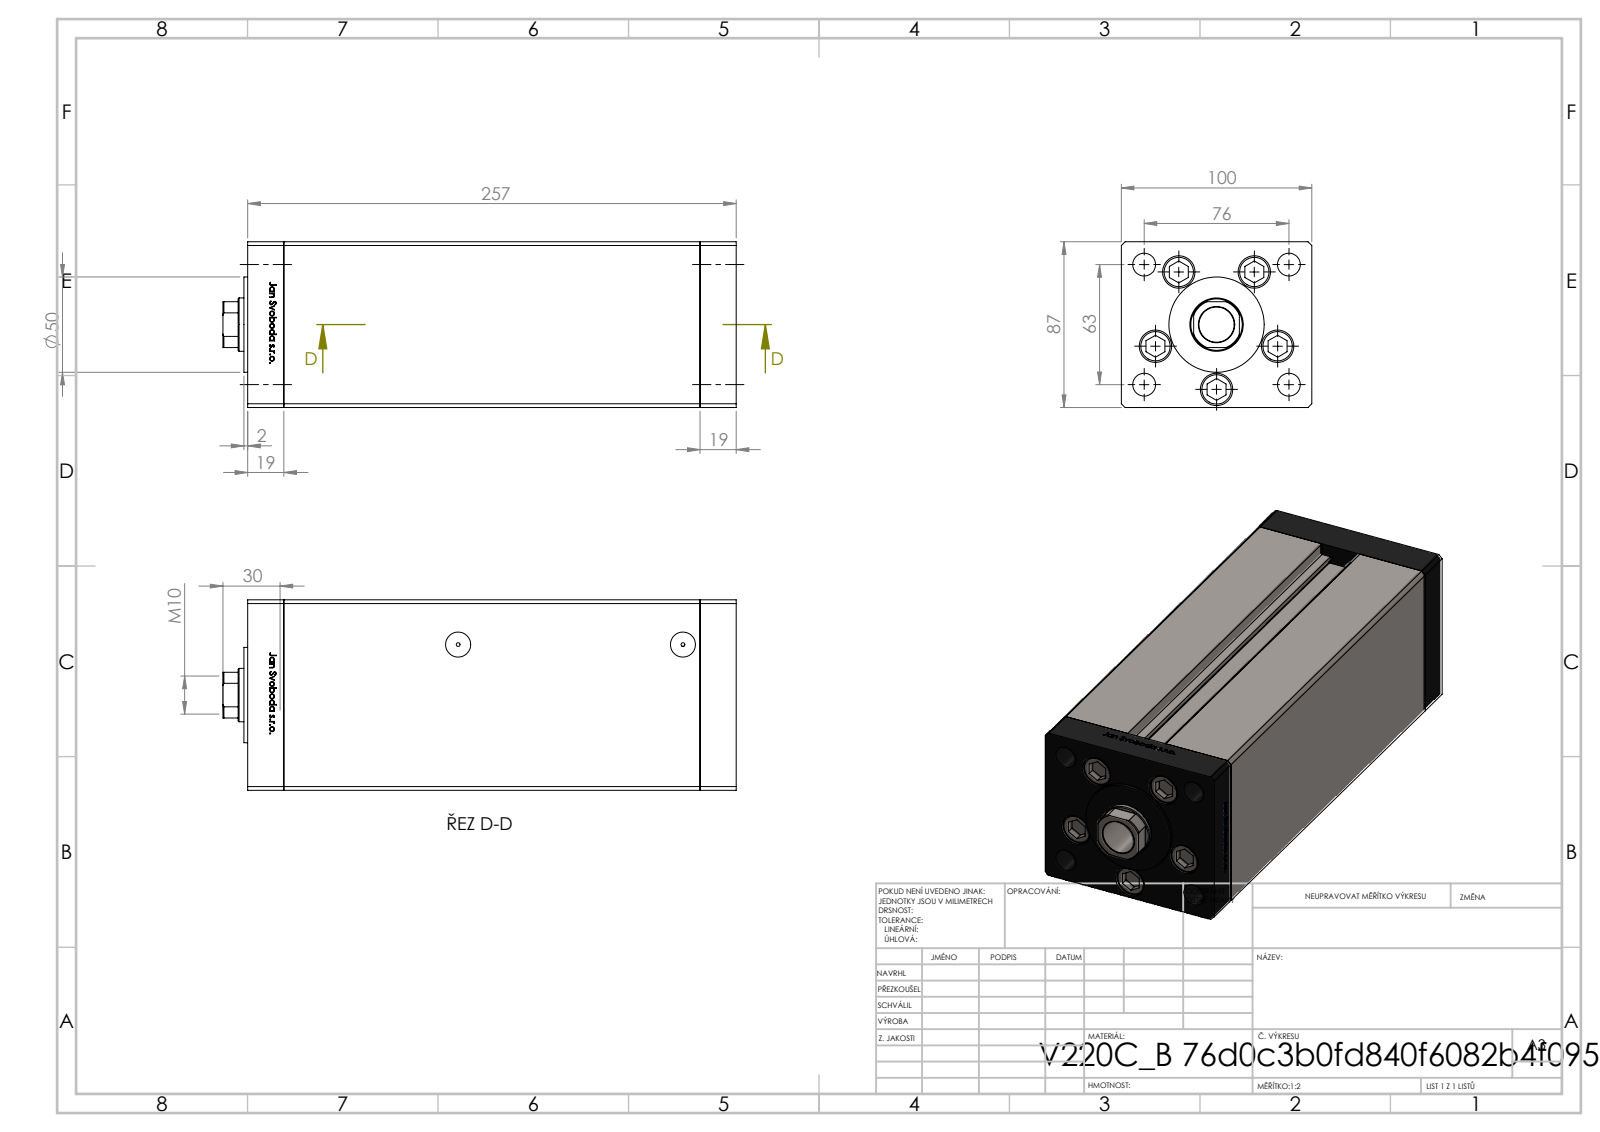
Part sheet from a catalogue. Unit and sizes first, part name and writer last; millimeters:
Units: millimetres
Overall size (bounding box): 269.5 × 100 × 87
Round holes (diameter × count): ⌀13.5 ×7, ⌀17 ×5, ⌀12 ×4, ⌀2 ×2, ⌀13.16 ×2, ⌀18.5 ×1, ⌀28 ×1
Round bosses / shafts (diameter × count): ⌀8 ×5, ⌀17 ×2, ⌀50 ×1
Partial cylindrical surfaces — rounded edges, fillets, slot ends (radius × count): R0.93 ×2, R13.5 ×1
Main face-to-face distances: 100, 87, 19, 218.5, 237.5, 34.25, 256.5, 15.25, 203.25, 222.25
Hole centre spacings: 34, 18.59, 39.64, 49.36, 57.95, 21.03, 38.08, 39.27
Volume: 1 933 000 mm³ · Surface area: 250 047 mm²
Bodies: 14 solids, 1185 faces (464 planar, 147 cylindrical, 574 other)
Part name (STEP PRODUCT): V220C_B MIDDLE; V220C_FRONT_B; V220C_VC_B; ALLEN BOLT (+1 more)
STEP written by: SolidWorks 2019 (CONFIG_CONTROL_DESIGN)
